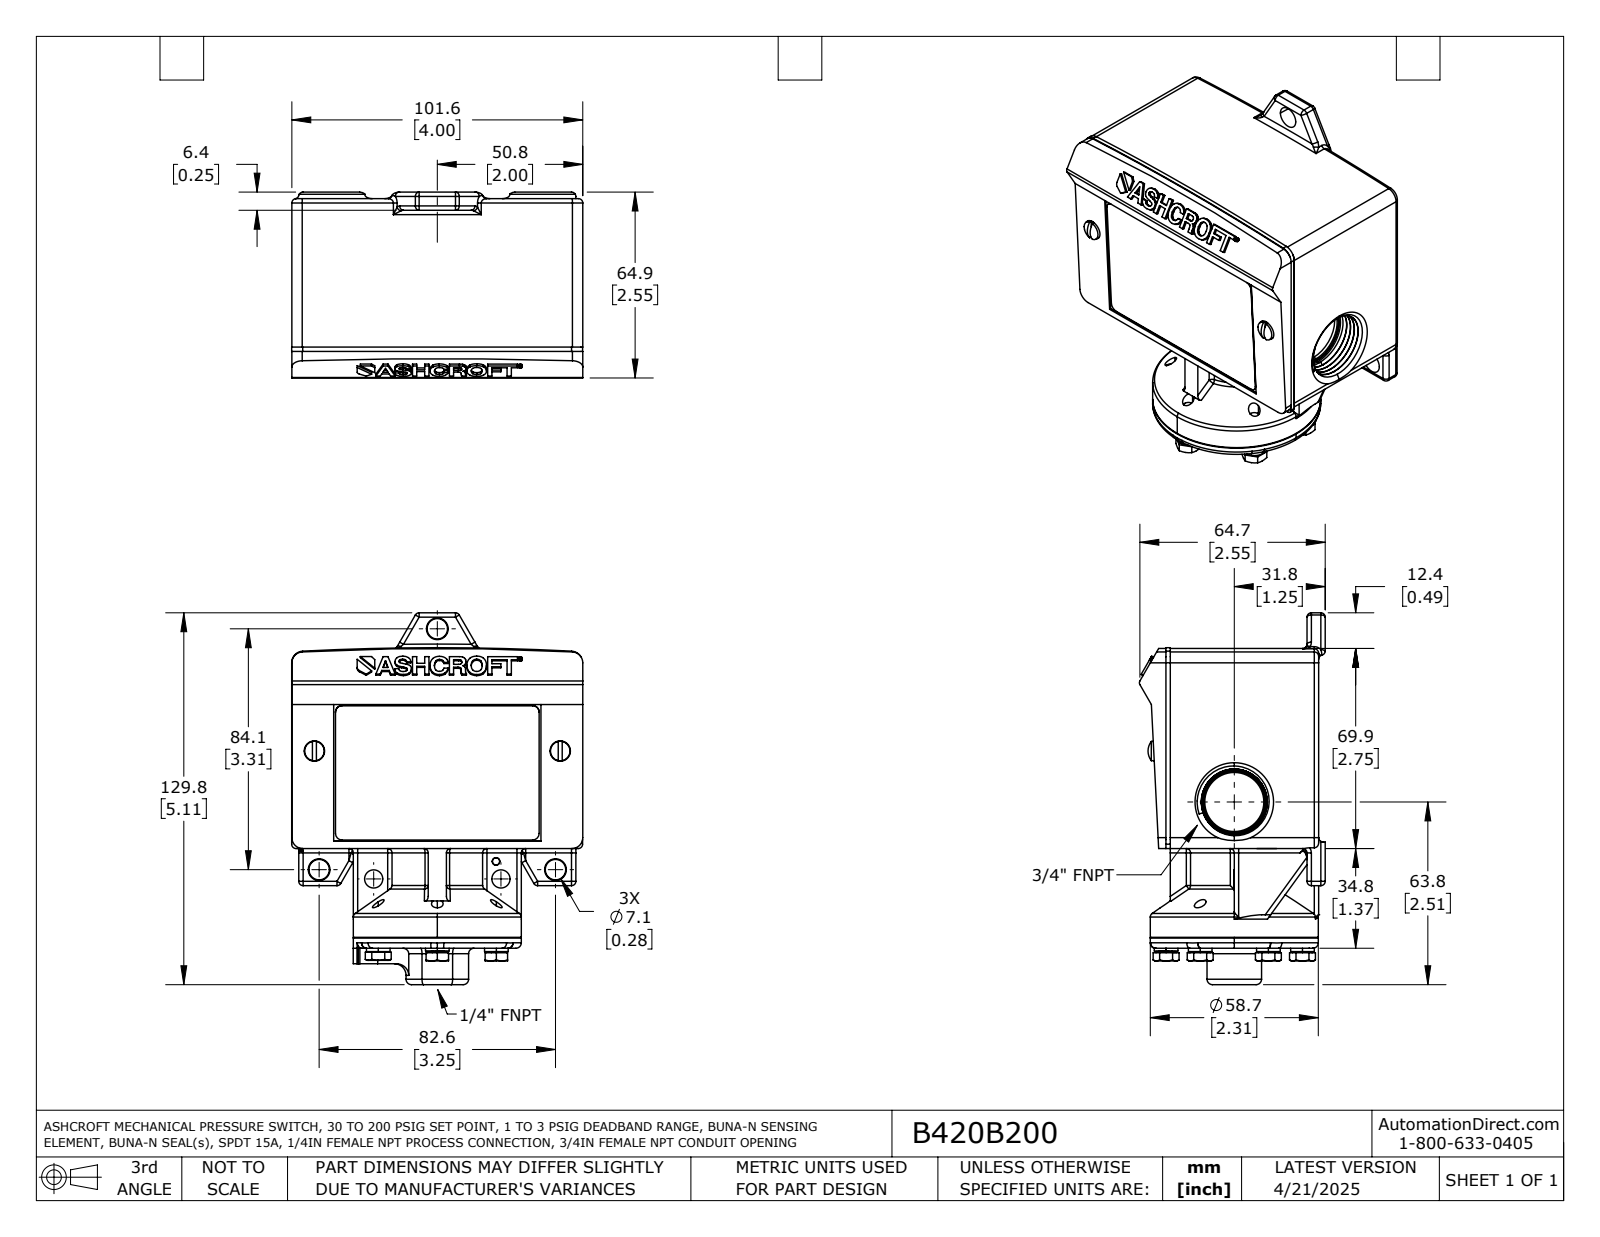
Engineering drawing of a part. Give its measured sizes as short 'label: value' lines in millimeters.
name: B420B200
written by: SolidWorks 2021 (AUTOMOTIVE_DESIGN)
unit: mm
bodies: 2 solids, 1259 faces (345 planar, 472 cylindrical, 442 other)
size: 129.8 × 101.7 × 64.9
volume: 468 200 mm³; area: 54 520 mm²
holes: 6× ⌀4.1, 5× ⌀4.9, 5× ⌀5.3, 4× ⌀4.7, 2× ⌀7.1, 1× ⌀11.6, 1× ⌀20.6
bosses: 6× ⌀8.3, 6× ⌀7.1, 5× ⌀4.8, 2× ⌀6.9, 2× ⌀6.4, 1× ⌀58.7
rounds: 92× R1.5, 5× R0.8, 4× R1.9, 4× R2.3, 4× R3.8, 2× R0.3, 2× R2.4, 2× R4.1
face distances: 101.6, 0.4, 34.8, 2.3, 99.3, 11.2, 90.4, 88.1, 8.9, 21.5
hole spacings: 23.8, 41.2, 47.6, 23.8, 85.9
